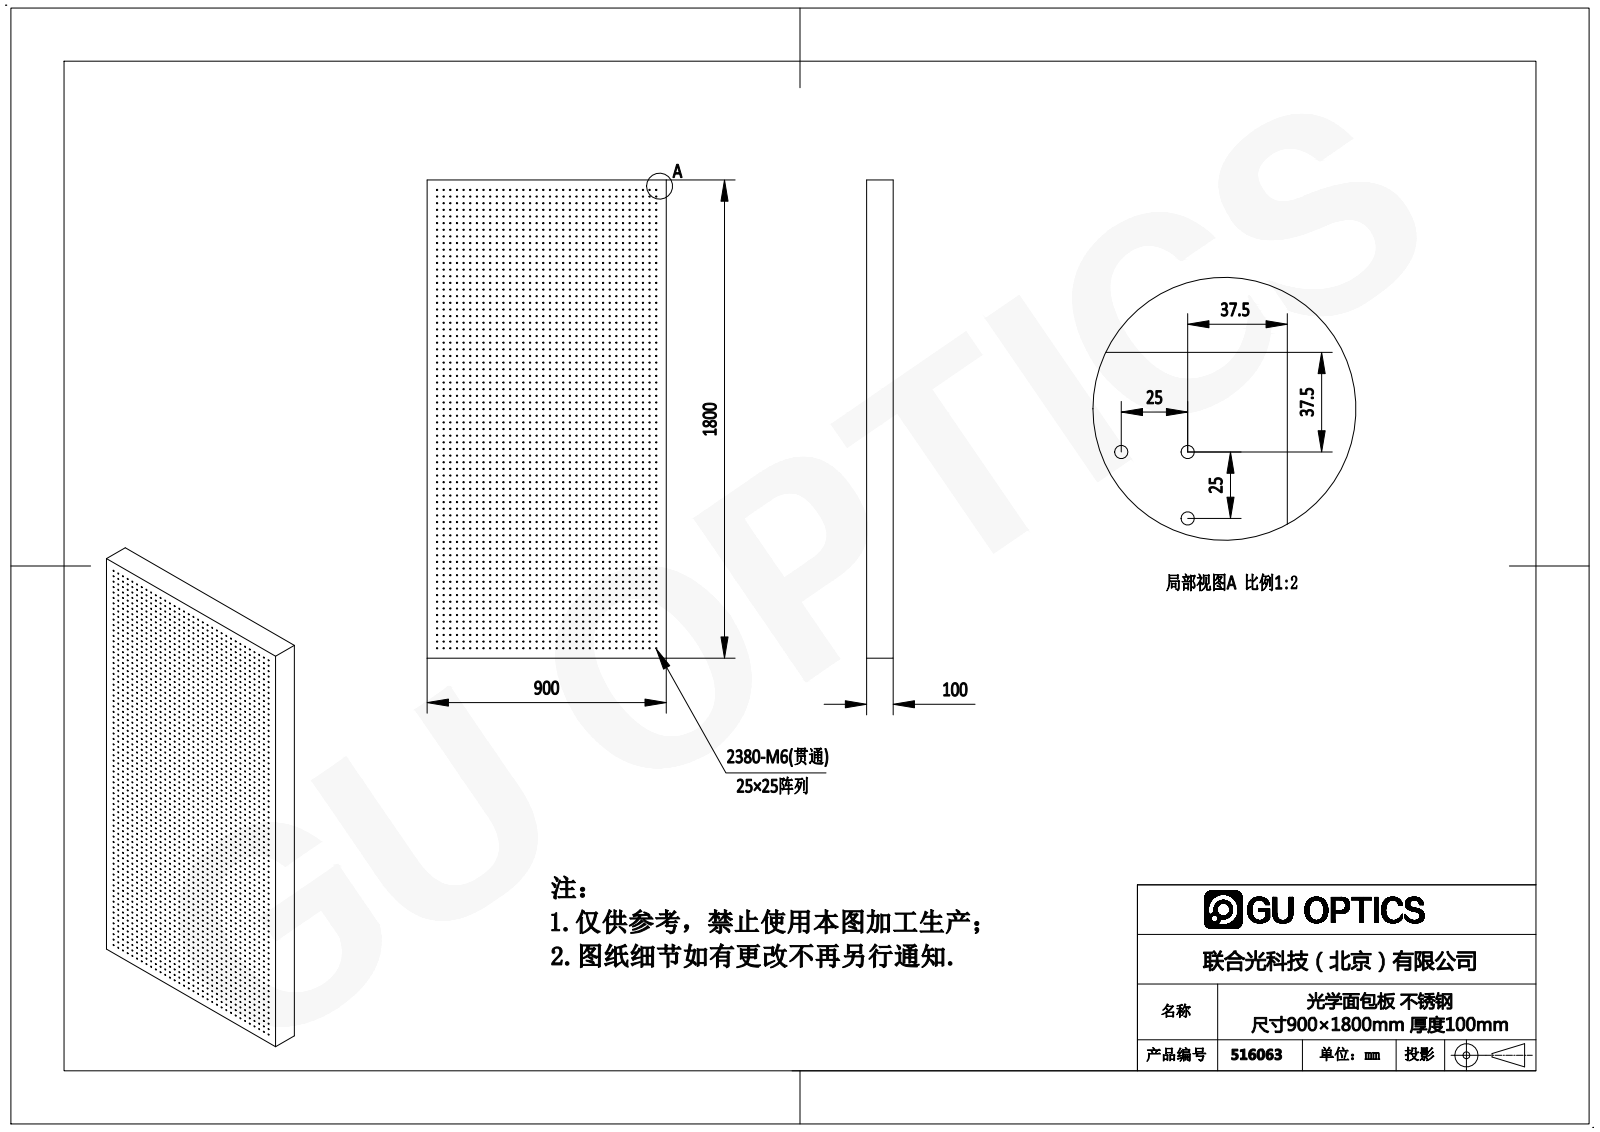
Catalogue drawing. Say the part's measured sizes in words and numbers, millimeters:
The part is named "516063". Its 3-D file was written by "SolidWorks 2020 (CONFIG_CONTROL_DESIGN)". It is 1 solid with 7200 faces: 2424 planar, 4776 cylindrical and 0 other. Overall it measures 1800 by 900 by 100 millimeters. Its volume is 155 500 000 cubic millimeters and its surface area 4 165 000 square millimeters. Round holes: 2380 of diameter 5.3. Partial cylindrical surfaces (rounded edges, fillets, slot ends): 4 of radius 2, 4 of radius 3, 4 of radius 11. The main face-to-face distances are 100, 874, 6, 94, 1774, 95, 89, 5, 13, 887. The hole center spacings are 79.06, 35.36, 50, 55.9, 25, 127.48, 90.14, 70.71.
